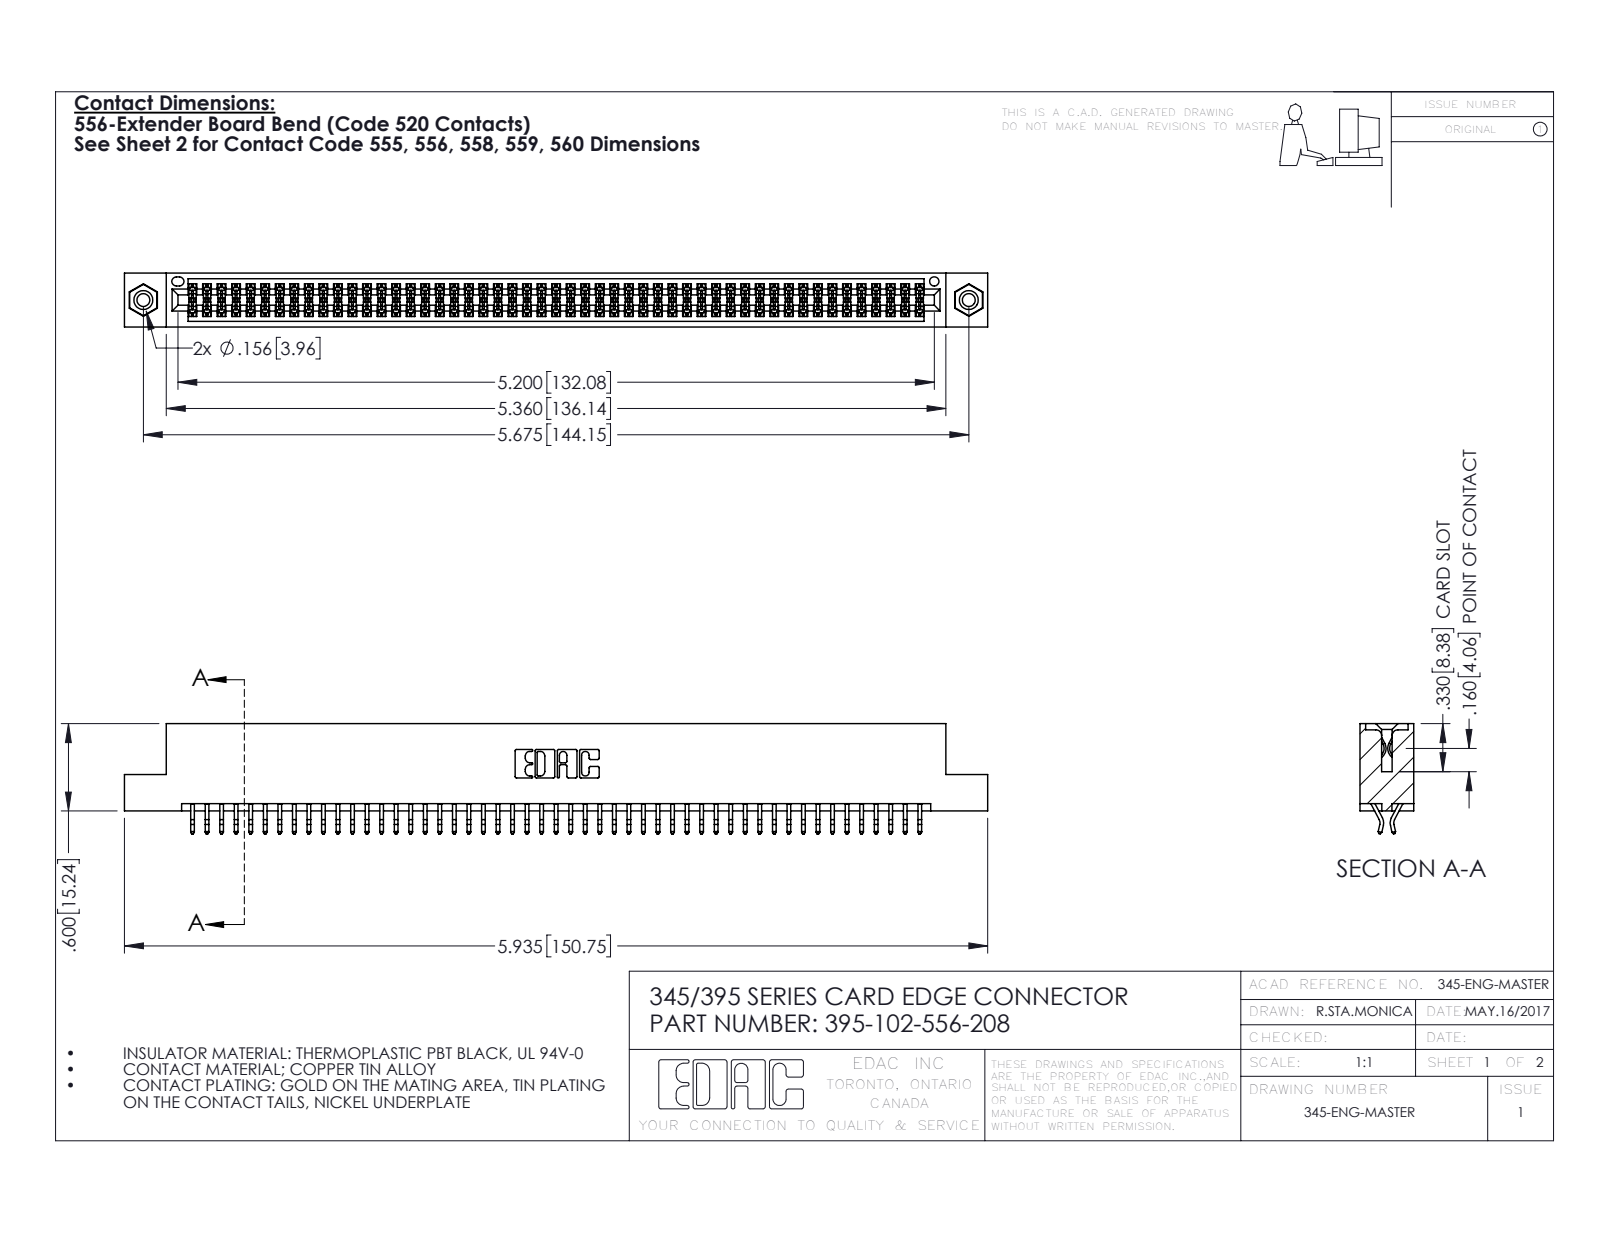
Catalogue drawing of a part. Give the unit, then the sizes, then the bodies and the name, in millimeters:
Units: millimetres
Overall size (bounding box): 150.7 × 19.2 × 9.4
Round holes (diameter × count): ⌀2.3 ×2, ⌀3.2 ×2, ⌀4 ×2, ⌀1.6 ×1
Round bosses / shafts (diameter × count): ⌀3.9 ×2
Partial cylindrical surfaces — rounded edges, fillets, slot ends (radius × count): R0.2 ×153, R0.3 ×22, R0.2 ×6, R0.8 ×6, R0.7 ×3, R0.3 ×2, R0.4 ×2, R0.5 ×2
Main face-to-face distances: 1.8, 7.6, 9.4, 5.1, 0.6, 2.5, 6.9, 5.7, 4.4, 3.8
Hole centre spacings: 6.9, 138.2, 144.1
Volume: 14 700 mm³ · Surface area: 21 850 mm²
Bodies: 105 solids, 5898 faces (3886 planar, 1996 cylindrical, 16 other)
Part name (STEP PRODUCT): 345-292-001_556 Tail; 345-250-001_345-250-003-102; 345 Part_Flush Mounting Lugs - 0.156 Dia-TI; 395-102-556-208
STEP written by: SolidWorks 2016 (CONFIG_CONTROL_DESIGN)
